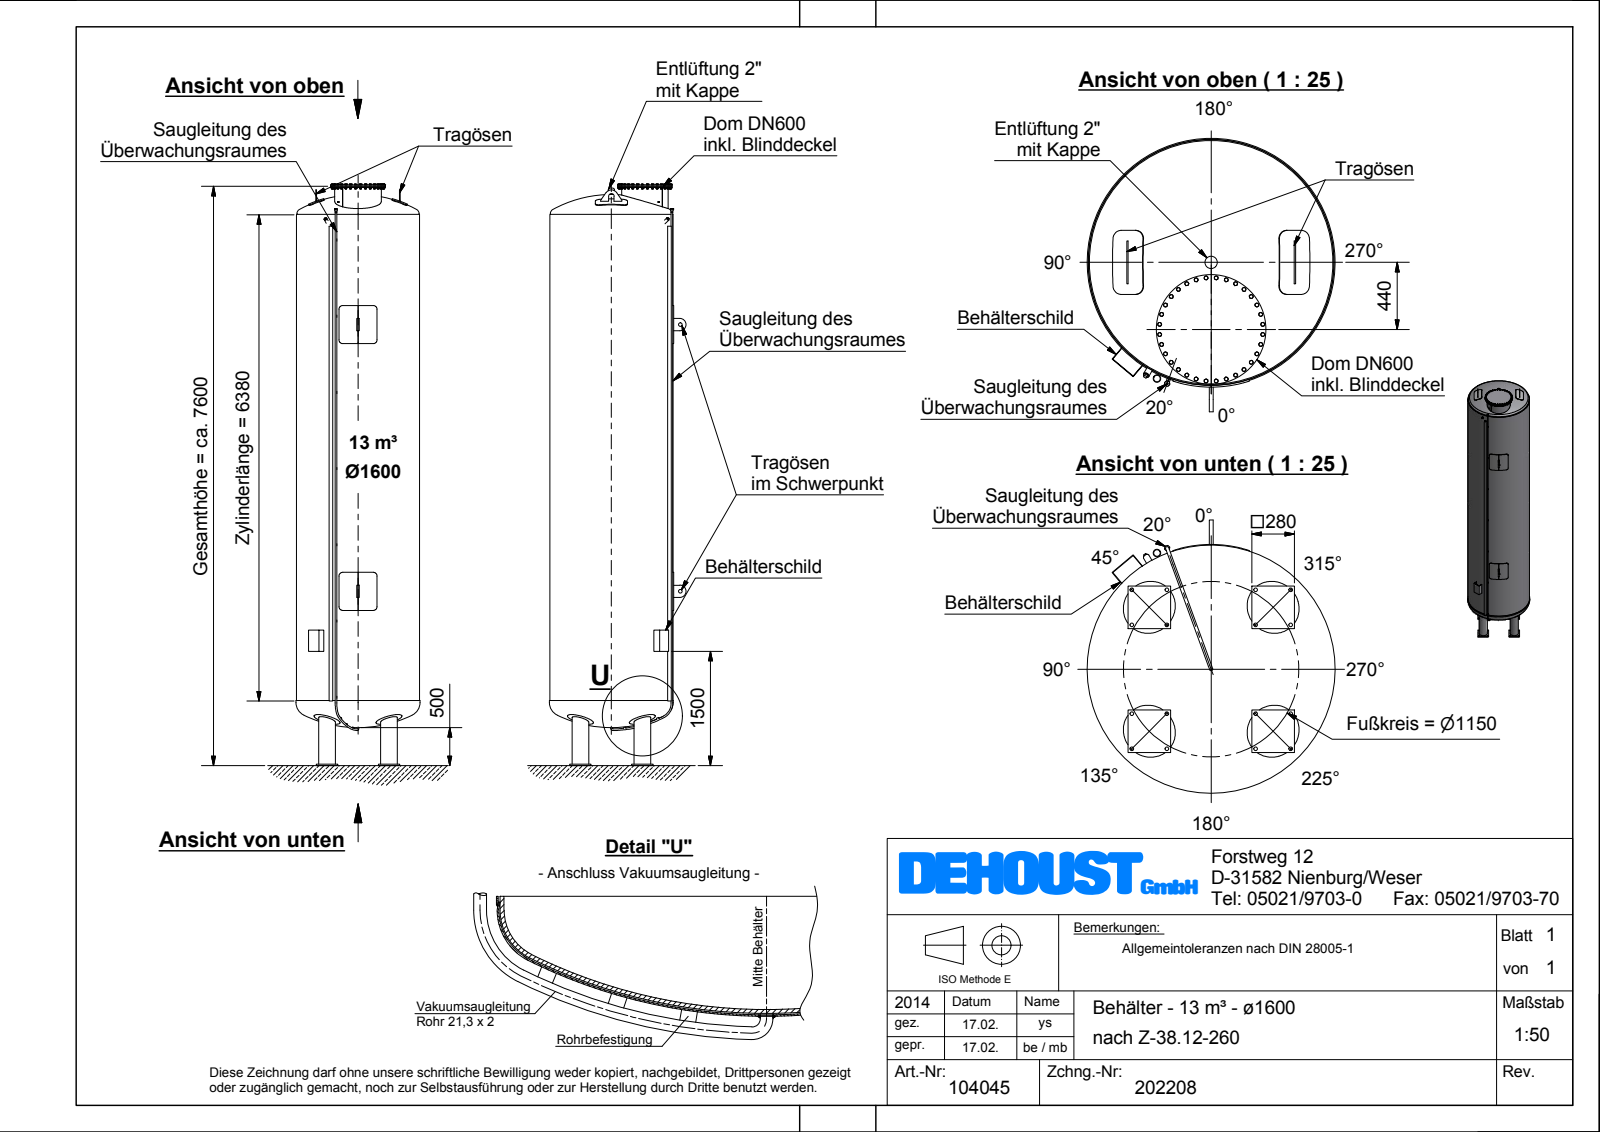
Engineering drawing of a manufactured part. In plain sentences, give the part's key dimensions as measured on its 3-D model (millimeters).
The part is named "Z-38_12-260_Beh\\S\\dlter_\\S\\x1600_013m\\S\\3_Dichte=1,0". Its 3-D file was written by "Autodesk Inventor 2012 (AUTOMOTIVE_DESIGN)". It is 11 solids with 1203 faces: 721 planar, 158 cylindrical and 324 other. Overall it measures 7629.34 by 1721.38 by 1626 millimeters. Its volume is 13 660 000 000 cubic millimeters and its surface area 49 250 000 square millimeters. Round holes: 4 of diameter 203.1, 1 of diameter 598, 1 of diameter 1590. Round bosses or shafts: 32 of diameter 22.5, 32 of diameter 16, 4 of diameter 350, 4 of diameter 219.1, 2 of diameter 21.3, 1 of diameter 1626, 1 of diameter 1616, 1 of diameter 1600. Partial cylindrical surfaces (rounded edges, fillets, slot ends): 8 of radius 50, 8 of radius 56, 2 of radius 35, 2 of radius 80, 2 of radius 85, 1 of radius 818. The main face-to-face distances are 384.69, 349.69, 35, 7234.65, 7584.34, 7619.34, 20, 7564.34, 7214.65, 7599.34. The hole center spacings are 575, 813.17, 407.96, 939.16, 1150, 440.
